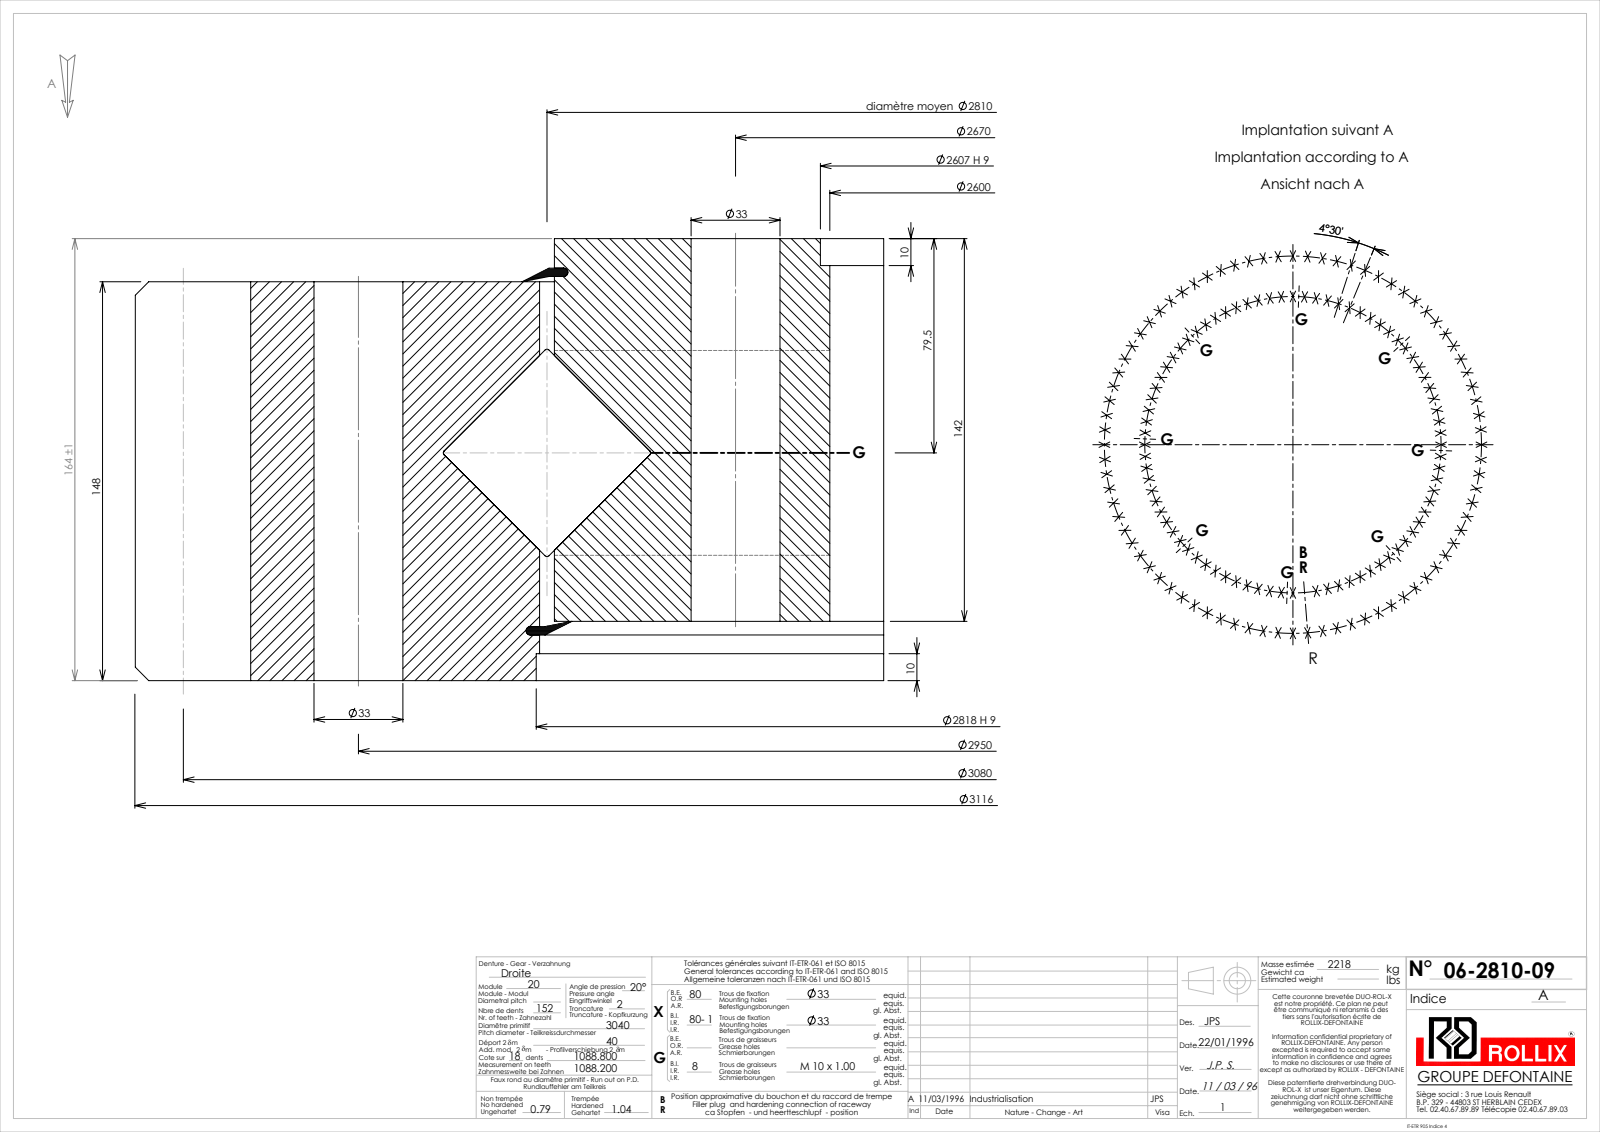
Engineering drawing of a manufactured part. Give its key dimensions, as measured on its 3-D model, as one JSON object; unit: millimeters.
{"part_name": "06-2810-09", "step_written_by": "SolidWorks 2016 (CONFIG_CONTROL_DESIGN)", "units": "millimeters", "bodies": {"solids": 5, "faces": 1335, "planar": 320, "cylindrical": 659, "other": 356}, "overall_size": [3115.68, 3115.68, 164], "volume_mm3": 259300000, "surface_area_mm2": 14130000, "round_holes": [[33, 159], [9, 8], [2600, 1], [2607, 1], [2815.5, 1], [2818, 1]], "round_bosses_or_shafts": [[2804.5, 1], [55, 1]], "partial_cylinders_radius": [[1515, 1], [1558, 1]], "face_to_face_distances": [148, 22, 126, 164, 142, 16, 1.95, 127.95, 5.05, 131.05], "hole_center_spacings": [115.82, 800.75, 911.6, 461.48, 231.45, 575.52, 346.74, 688.66]}
